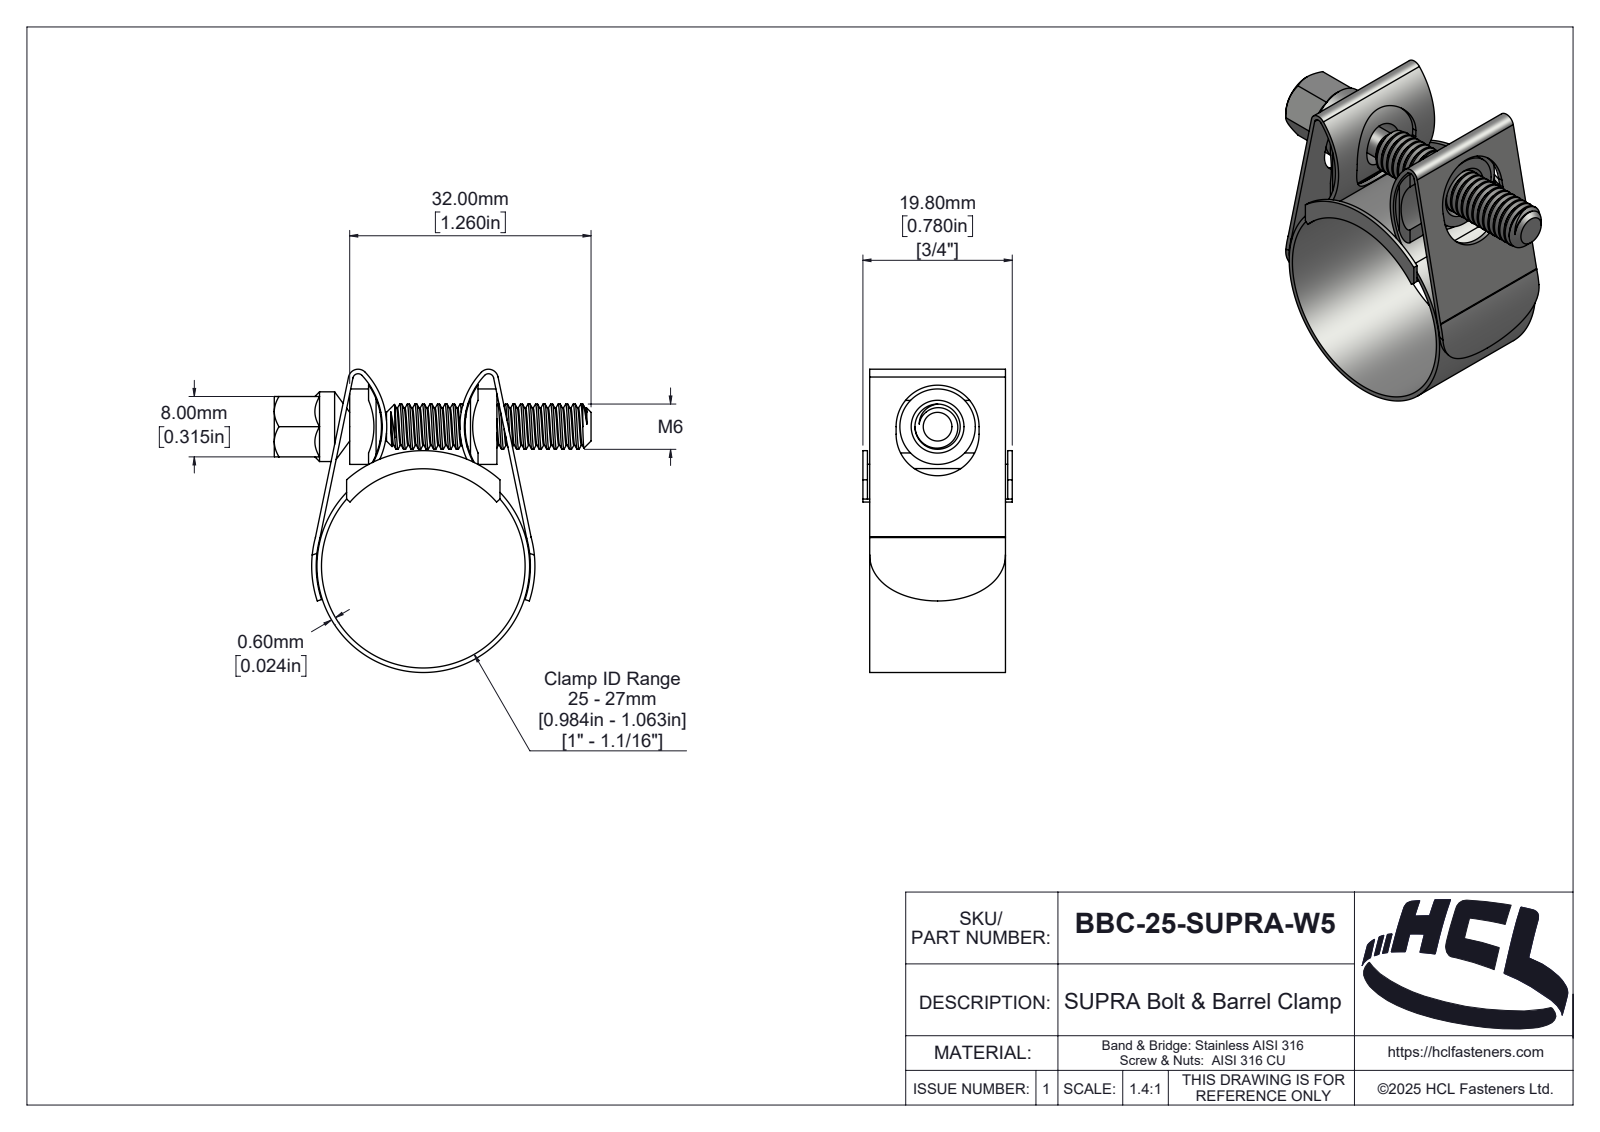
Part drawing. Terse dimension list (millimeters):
name: BBC-25-SUPRA-W5
written by: SolidWorks 2025 (AUTOMOTIVE_DESIGN)
unit: mm
bodies: 5 solids, 288 faces (44 planar, 164 cylindrical, 80 other)
size: 42 × 40.19 × 19.8
volume: 3 590 mm³; area: 8 601 mm²
holes: 1× ⌀27
bosses: 1× ⌀10, 1× ⌀9.24, 1× ⌀6, 1× ⌀3.8
rounds: 4× R1, 2× R0.7, 2× R1.3, 2× R2, 2× R2.6, 2× R5.5, 2× R8.84, 2× R9.84
face distances: 0.6, 0.9, 18.9, 18, 19.2, 18.3, 2.5, 17.02, 8, 18.6
